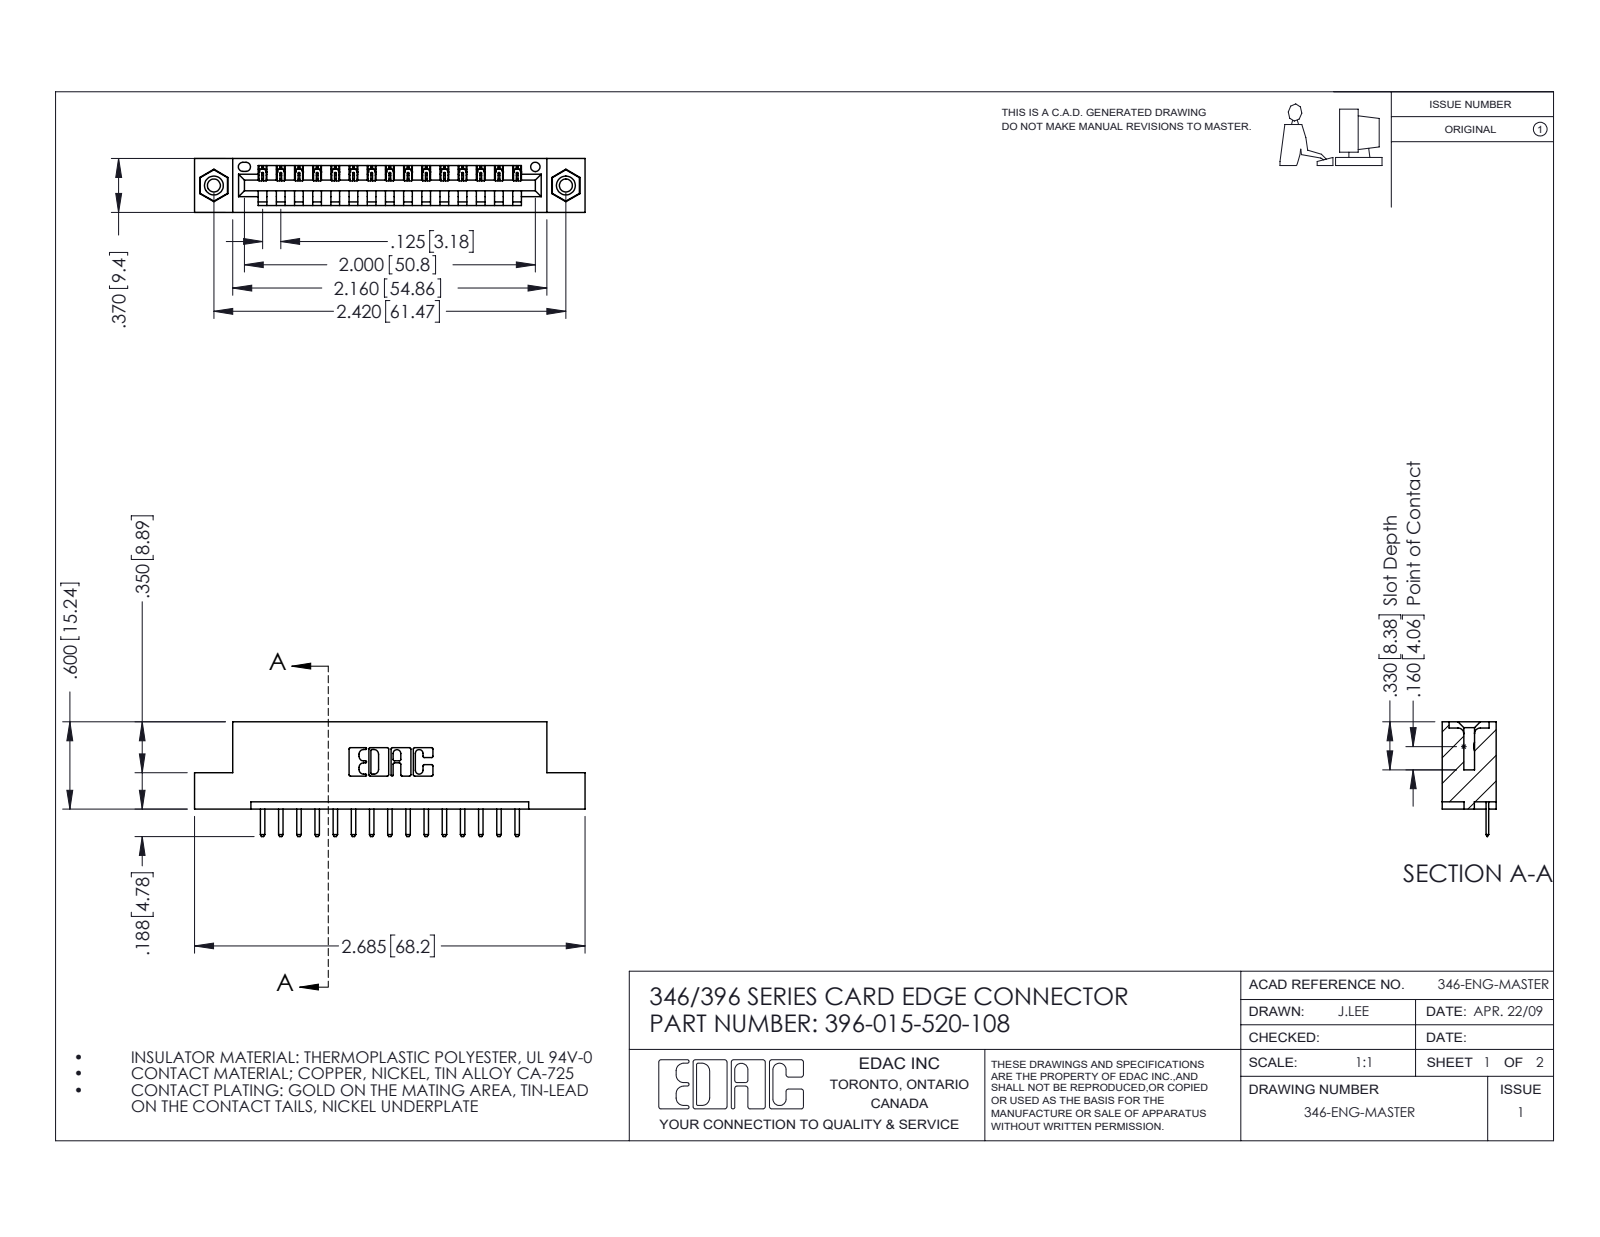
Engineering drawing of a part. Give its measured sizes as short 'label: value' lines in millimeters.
name: 346 Part_Flush Mounting Lugs - 0.156 Dia-TI; 396-015-520-108; 345-292-001_345-293-120; 345-250-001_345-250-003-102
written by: SolidWorks 2016 (CONFIG_CONTROL_DESIGN)
unit: mm
bodies: 18 solids, 1112 faces (738 planar, 358 cylindrical, 16 other)
size: 68.2 × 20 × 9.4
volume: 6 290 mm³; area: 7 452 mm²
holes: 2× ⌀2.3, 2× ⌀3.2, 2× ⌀4, 1× ⌀1.6
bosses: 2× ⌀3.9
rounds: 32× R0.3, 30× R0.2, 22× R0.3, 6× R0.2, 6× R0.8, 3× R0.7, 2× R0.8, 2× R1
face distances: 9.4, 6.4, 1.2, 8.2, 3.8, 5.6, 2.5, 4.4, 1.8, 7.6
hole spacings: 6.2, 56.2, 61.5
